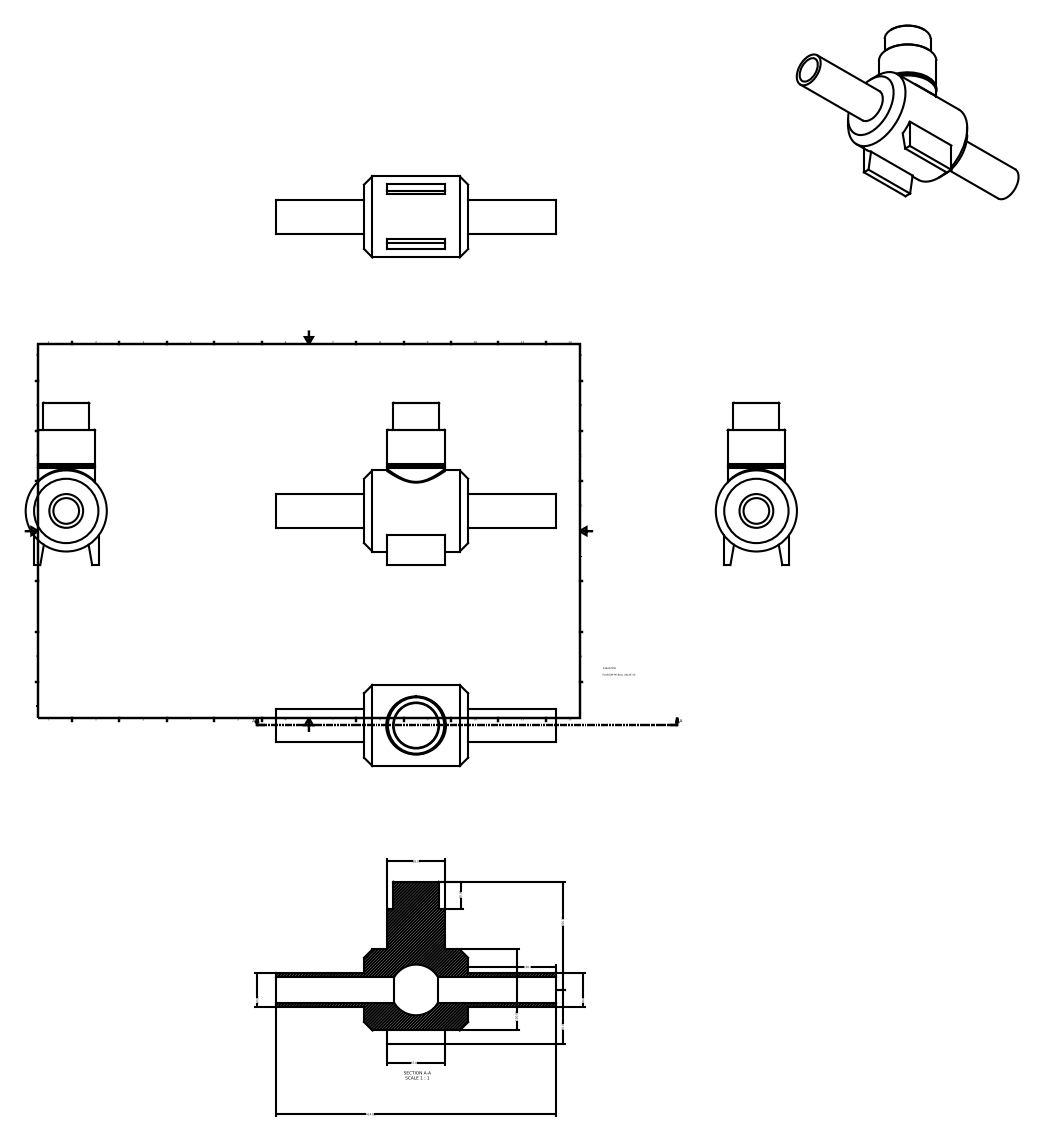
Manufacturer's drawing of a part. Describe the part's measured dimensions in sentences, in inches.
The part is named "436207050". Its 3-D file was written by "Autodesk Inventor 2015 (AUTOMOTIVE_DESIGN)". It is 1 solid with 33 faces: 16 planar, 9 cylindrical and 8 other. Overall it measures 16.299 by 9.449 by 4.724 inches. Its volume is 132.7 cubic inches and its surface area 325.1 square inches. Round holes: 1 of diameter 1.496. Round bosses or shafts: 1 of diameter 4.724, 1 of diameter 3.346, 1 of diameter 2.677, 1 of diameter 1.969. The main face-to-face distances are 6.063, 3.78, 1.319, 4.744, 1.575, 7.874, 9.449, 5.118, 6.437, 9.862.
